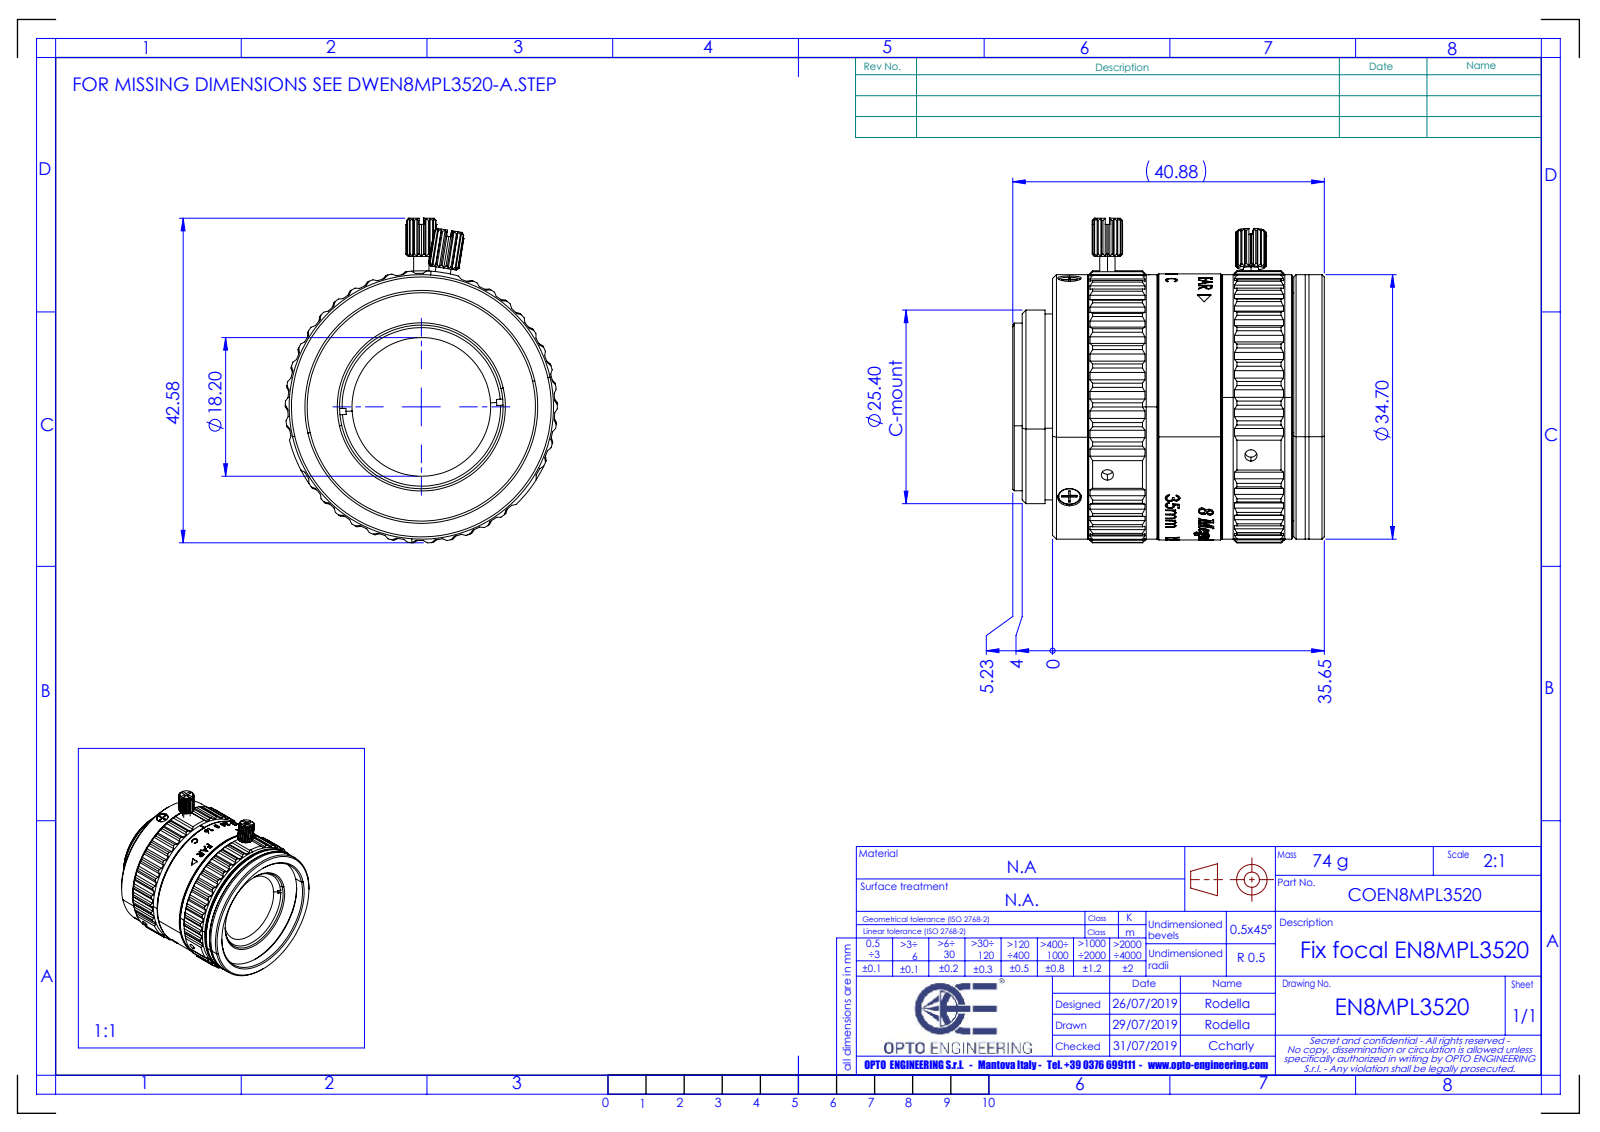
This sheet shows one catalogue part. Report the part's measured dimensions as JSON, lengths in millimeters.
{"part_name": "EN8MPL3520-02; EN8MPL3520-03; EN8MPL3520-04; EN8MPL3520-06 (+8 more)", "step_written_by": "PRO/ENGINEER BY PARAMETRIC TECHNOLOGY CORPORATION, 2015240 (CONFIG_CONTROL_DESIGN)", "units": "millimeters", "bodies": {"solids": 17, "faces": 1661, "planar": 672, "cylindrical": 300, "other": 689}, "overall_size": [42.34, 40.88, 35.67], "volume_mm3": 7216, "surface_area_mm2": 15133, "round_holes": [[1.6, 6], [2, 3], [3.1, 3], [0.8, 2], [1.25, 1], [2.3, 1], [16.6, 1], [18, 1], [18.2, 1], [19.46, 1], [19.5, 1], [20, 1]], "round_bosses_or_shafts": [[2, 4], [3, 3], [34.9, 1], [34.7, 1], [34.68, 1], [30.3, 1], [29.9, 1], [25.4, 1]], "partial_cylinders_radius": [[1.9, 2], [2, 2], [1.79, 1], [1.93, 1], [17.44, 1], [17.85, 1]], "face_to_face_distances": [32.65, 1.2, 4, 35.65, 1, 3, 31.65, 30.45, 2.2, 9.1], "hole_center_spacings": [9.6, 19.2]}
